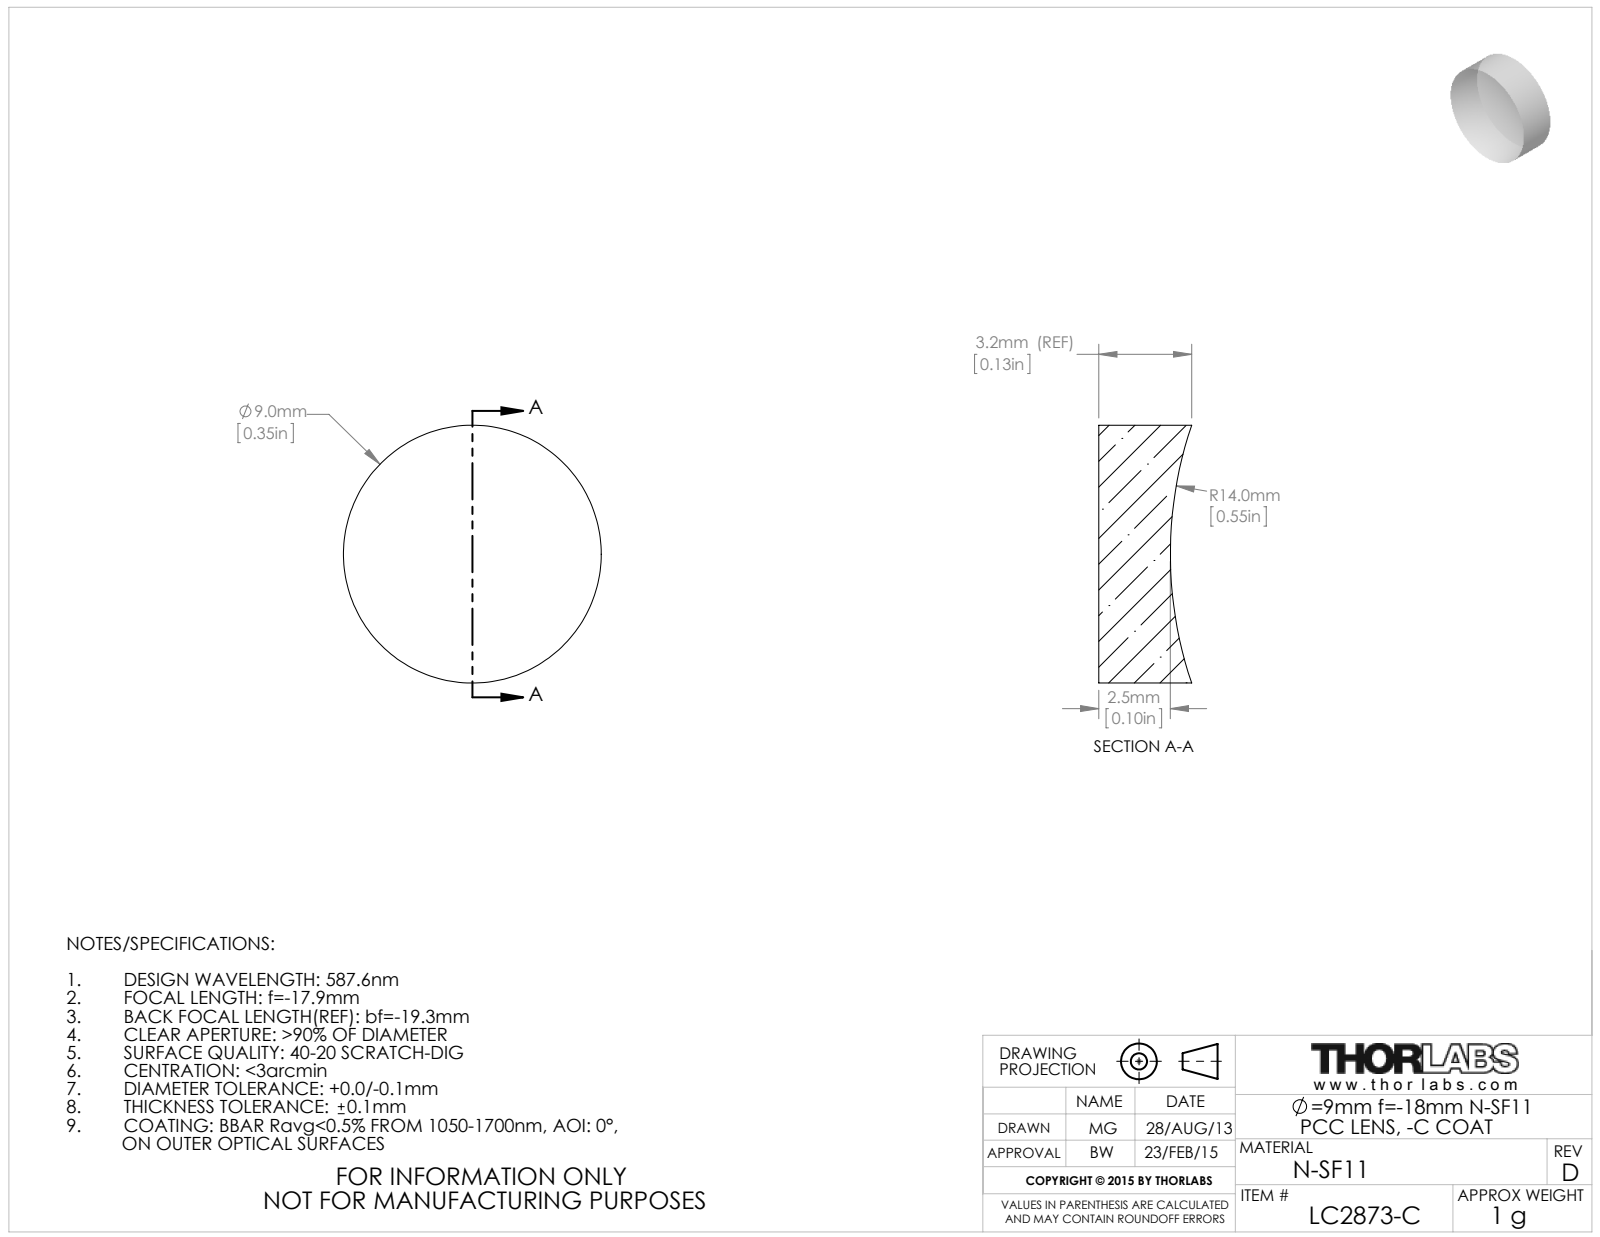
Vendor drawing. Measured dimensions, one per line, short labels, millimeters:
name: 5447-E0W
written by: SolidWorks 2014 (CONFIG_CONTROL_DESIGN)
unit: mm
bodies: 1 solid, 5 faces (1 planar, 2 cylindrical, 2 other)
size: 9 × 9 × 3.24
volume: 182 mm³; area: 221 mm²
bosses: 1× ⌀9
